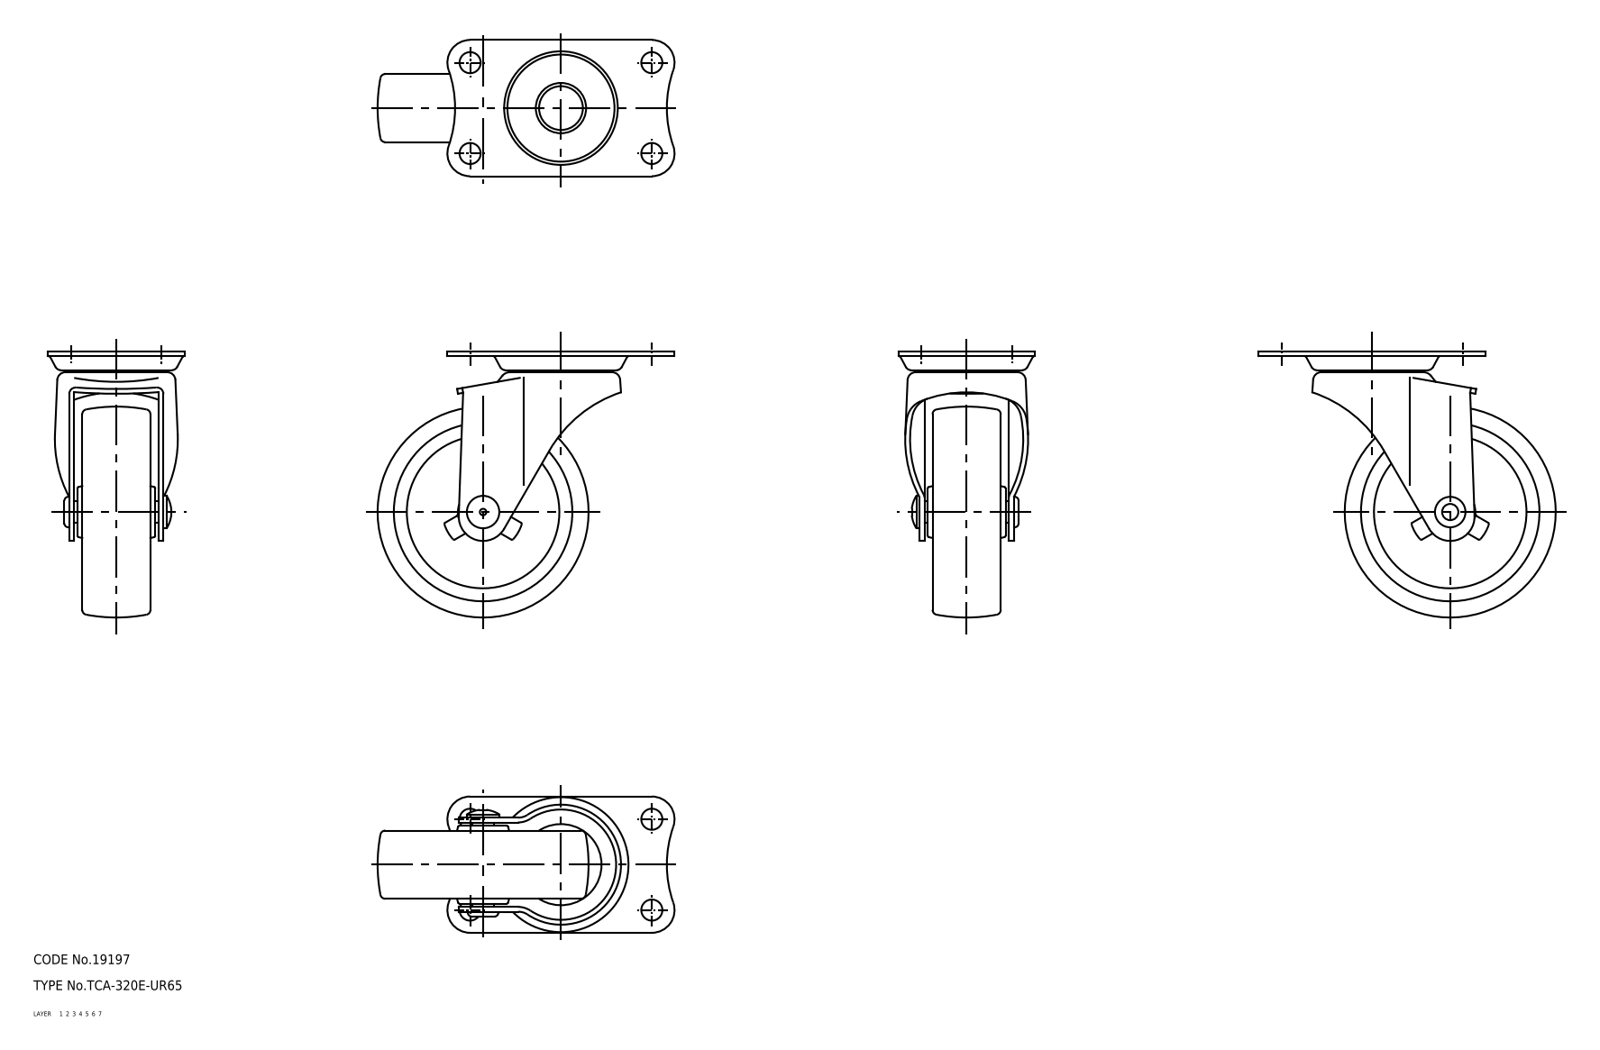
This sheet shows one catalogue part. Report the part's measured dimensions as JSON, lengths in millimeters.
{"part_name": "wheel; mounting plate; main shaft; axle (+1 more)", "step_written_by": "CADfix (AUTOMOTIVE_DESIGN)", "units": "millimeters", "bodies": {"solids": 5, "faces": 346, "planar": 0, "cylindrical": 0, "other": 346}, "overall_size": [91.5, 82, 42], "volume_mm3": 68450, "surface_area_mm2": 31070}
